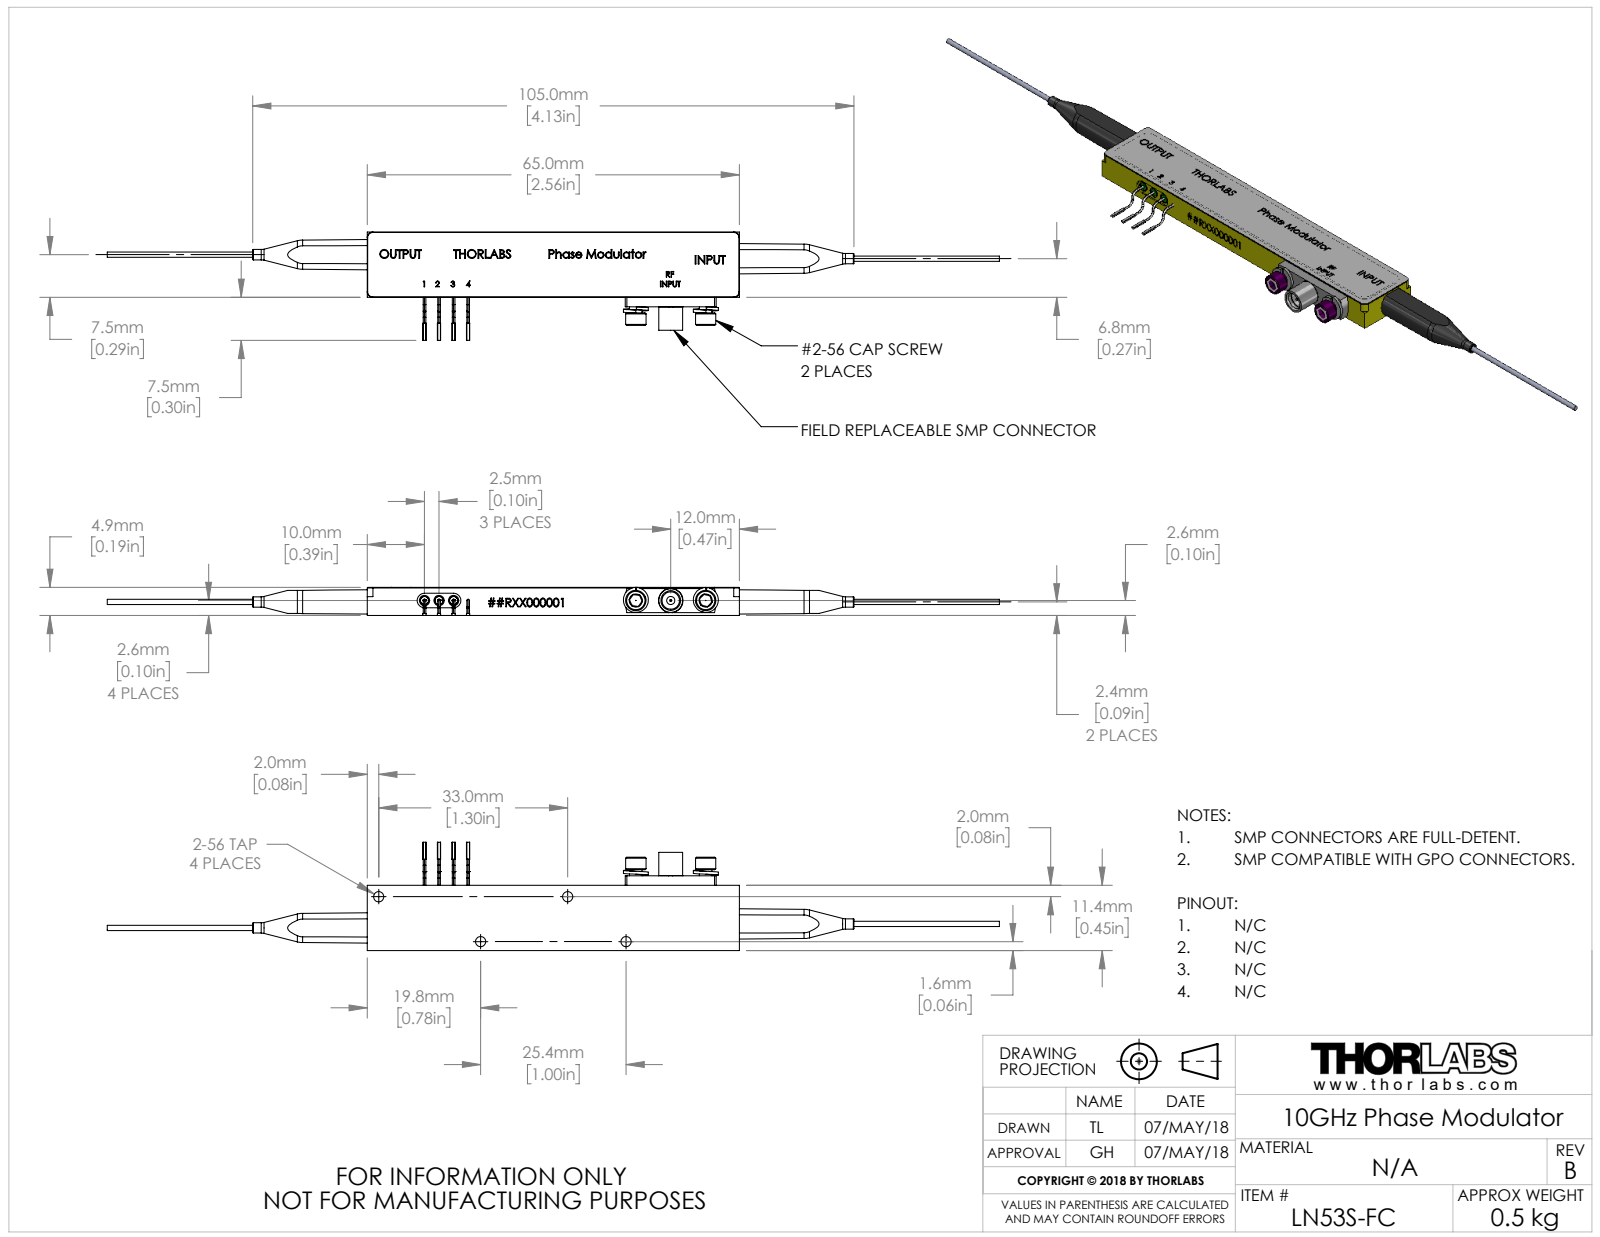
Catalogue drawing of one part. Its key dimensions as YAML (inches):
part_name: "19528-E0W"
step_written_by: "SolidWorks 2016 (CONFIG_CONTROL_DESIGN)"
units: inches
bodies: {solids: 0, faces: 536, planar: 259, cylindrical: 115, other: 162}
overall_size: [6.134, 0.744, 0.193]
round_holes:
  - {diameter: 0.07, count: 4}
  - {diameter: 0.071, count: 3}
  - {diameter: 0.103, count: 1}
  - {diameter: 0.12, count: 1}
  - {diameter: 0.125, count: 1}
round_bosses_or_shafts:
  - {diameter: 0.018, count: 4}
  - {diameter: 0.14, count: 2}
  - {diameter: 0.086, count: 2}
  - {diameter: 0.071, count: 2}
  - {diameter: 0.035, count: 2}
  - {diameter: 0.164, count: 1}
  - {diameter: 0.057, count: 1}
  - {diameter: 0.015, count: 1}
partial_cylinders:
  - {radius: 0.009, count: 12}
  - {radius: 0.035, count: 4}
  - {radius: 0.039, count: 4}
  - {radius: 0.05, count: 2}
  - {radius: 0.312, count: 1}
face_to_face_distances: [0.193, 0.449, 0.188, 0.19, 2.559, 0.065, 0.514, 0.02, 0.185, 0.165]
hole_center_spacings: [0.1, 0.2, 0.24, 0.506, 0.673, 0.766, 1, 1.299]
